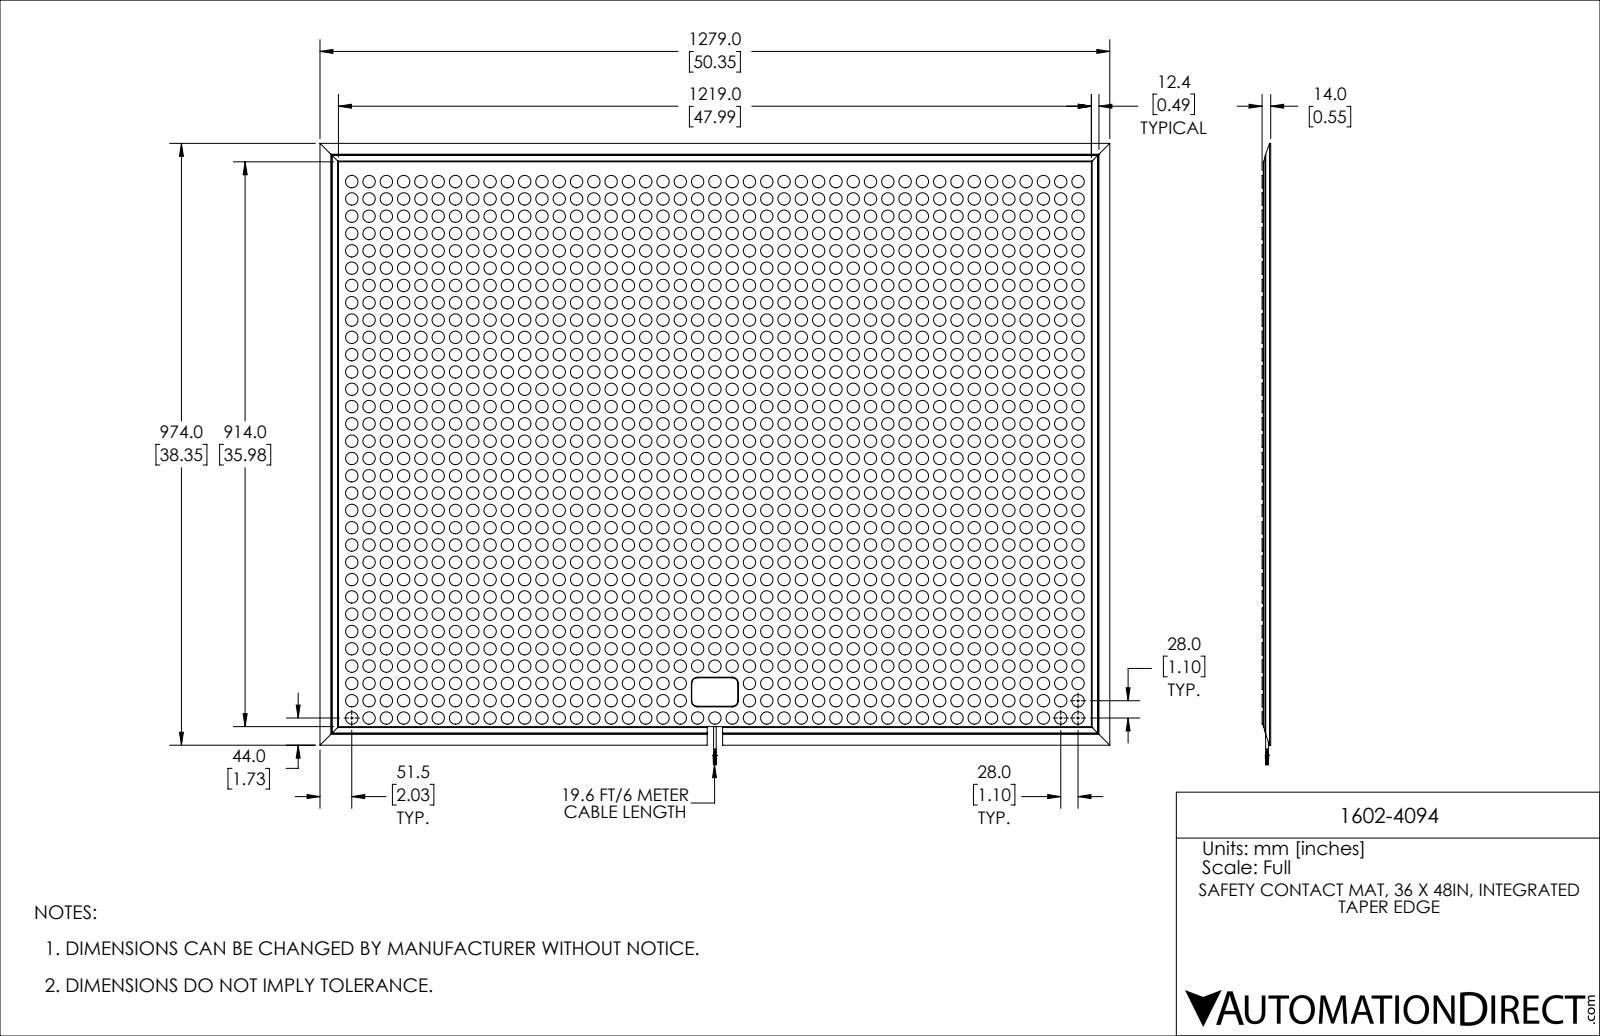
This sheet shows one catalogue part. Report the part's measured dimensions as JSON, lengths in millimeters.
{"part_name": "1602-4094", "step_written_by": "SolidWorks 2021 (AUTOMOTIVE_DESIGN)", "units": "millimeters", "bodies": {"solids": 1375, "faces": 5681, "planar": 2818, "cylindrical": 2822, "other": 41}, "overall_size": [1279, 1005.5, 14], "volume_mm3": 14920000, "surface_area_mm2": 3655000, "round_bosses_or_shafts": [[20, 1370], [1.2, 20], [0.8, 8], [4.4, 1]], "partial_cylinders_radius": [[10, 6], [1, 4]], "face_to_face_distances": [12, 2, 14, 914, 1219, 30, 3.4, 1.4, 10.6, 3.5]}
